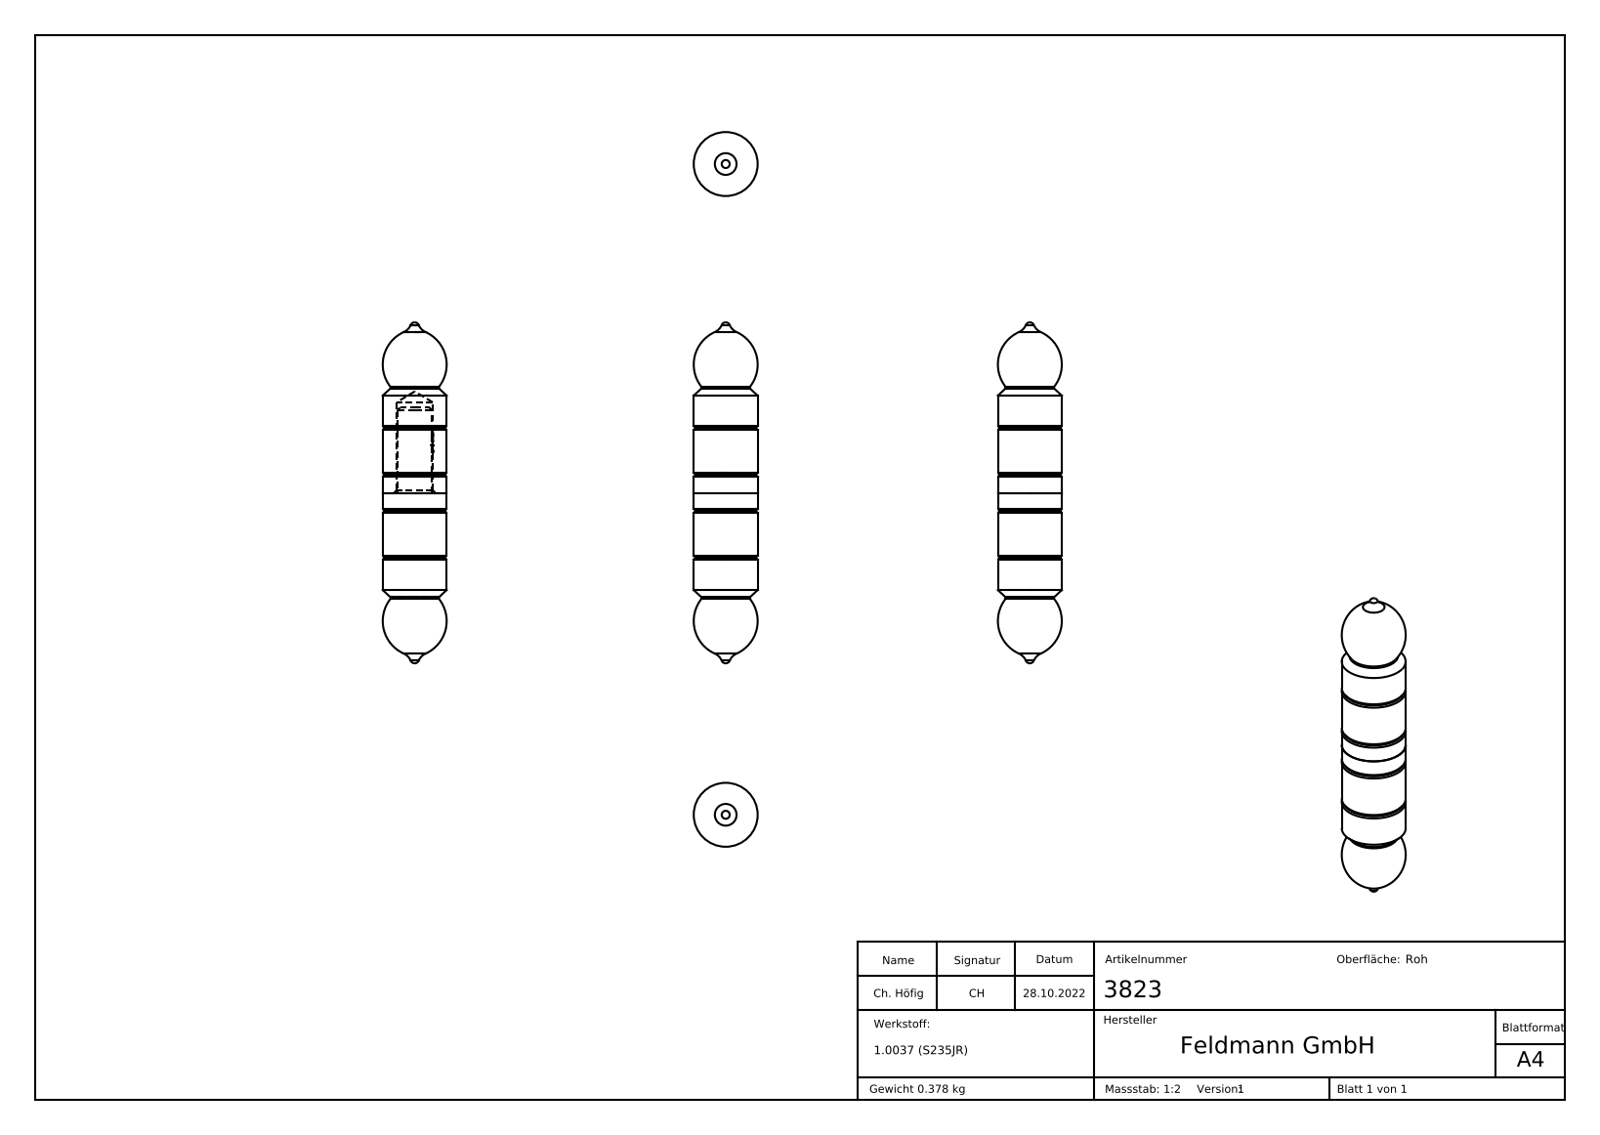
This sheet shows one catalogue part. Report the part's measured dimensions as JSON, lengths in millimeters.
{"part_name": "3823 Teil1_3823 Teil2; 3823; 3823 Teil1_3823 Teil1", "step_written_by": "SolidWorks 2018 (CONFIG_CONTROL_DESIGN)", "units": "millimeters", "bodies": {"solids": 2, "faces": 261, "planar": 91, "cylindrical": 30, "other": 140}, "overall_size": [128, 24, 24], "volume_mm3": 48499, "surface_area_mm2": 13031, "round_holes": [[13.5, 1]], "round_bosses_or_shafts": [[24, 1], [23, 1], [13, 1]], "partial_cylinders_radius": [[6.85, 1]], "face_to_face_distances": [32, 0.31, 0.32, 0.44, 2.49, 3.12, 2.06, 2.81, 0.41, 0.87]}
